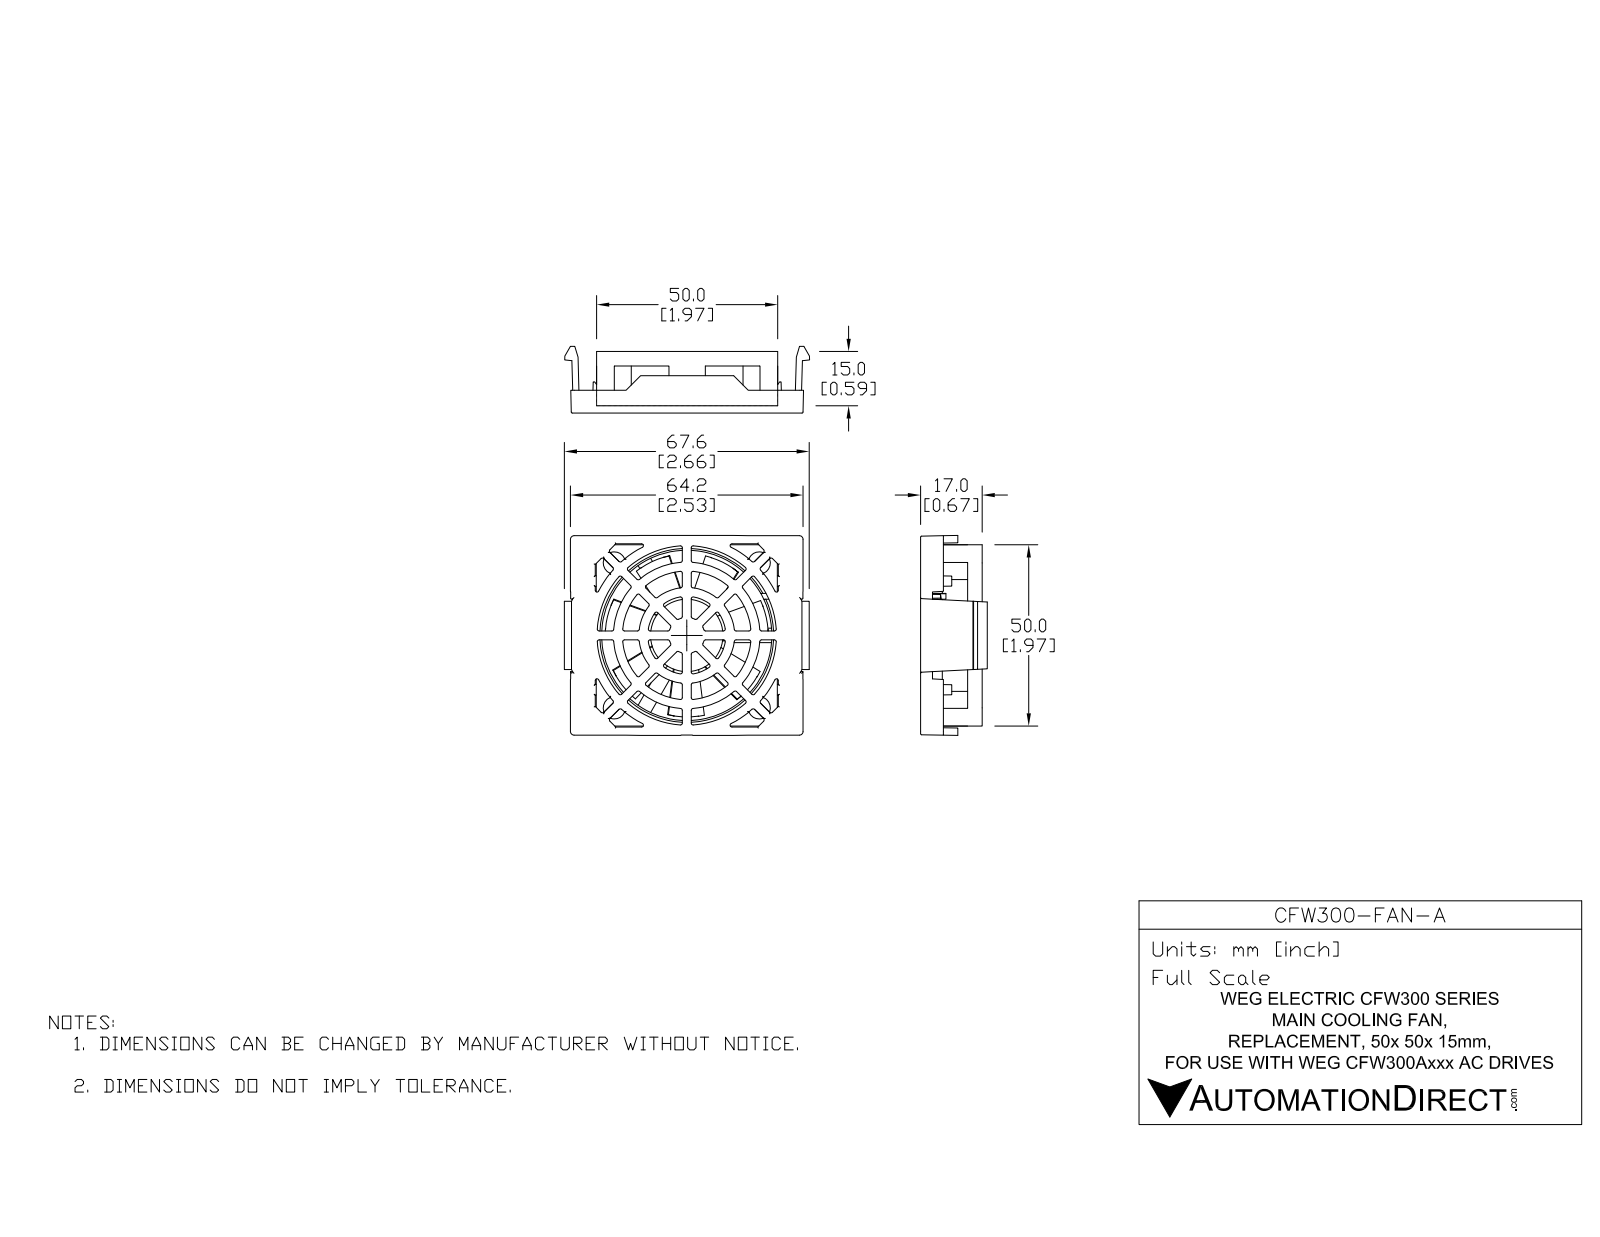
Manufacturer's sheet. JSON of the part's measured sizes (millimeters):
{"part_name": "113771363", "step_written_by": "SolidWorks 2017 (AUTOMOTIVE_DESIGN)", "units": "millimeters", "bodies": {"solids": 2, "faces": 967, "planar": 332, "cylindrical": 180, "other": 455}, "overall_size": [67.62, 55.16, 18.42], "volume_mm3": 21791, "surface_area_mm2": 22996, "round_holes": [[4.3, 4], [47, 1]], "round_bosses_or_shafts": [[25, 1], [20, 1]], "partial_cylinders_radius": [[0.3, 36], [0.5, 12], [1, 4], [5, 4], [22.5, 1], [25.5, 1]], "face_to_face_distances": [2, 15, 17, 2.03, 50, 4, 13, 1.7, 11, 3], "hole_center_spacings": [28.28, 40, 56.57]}
